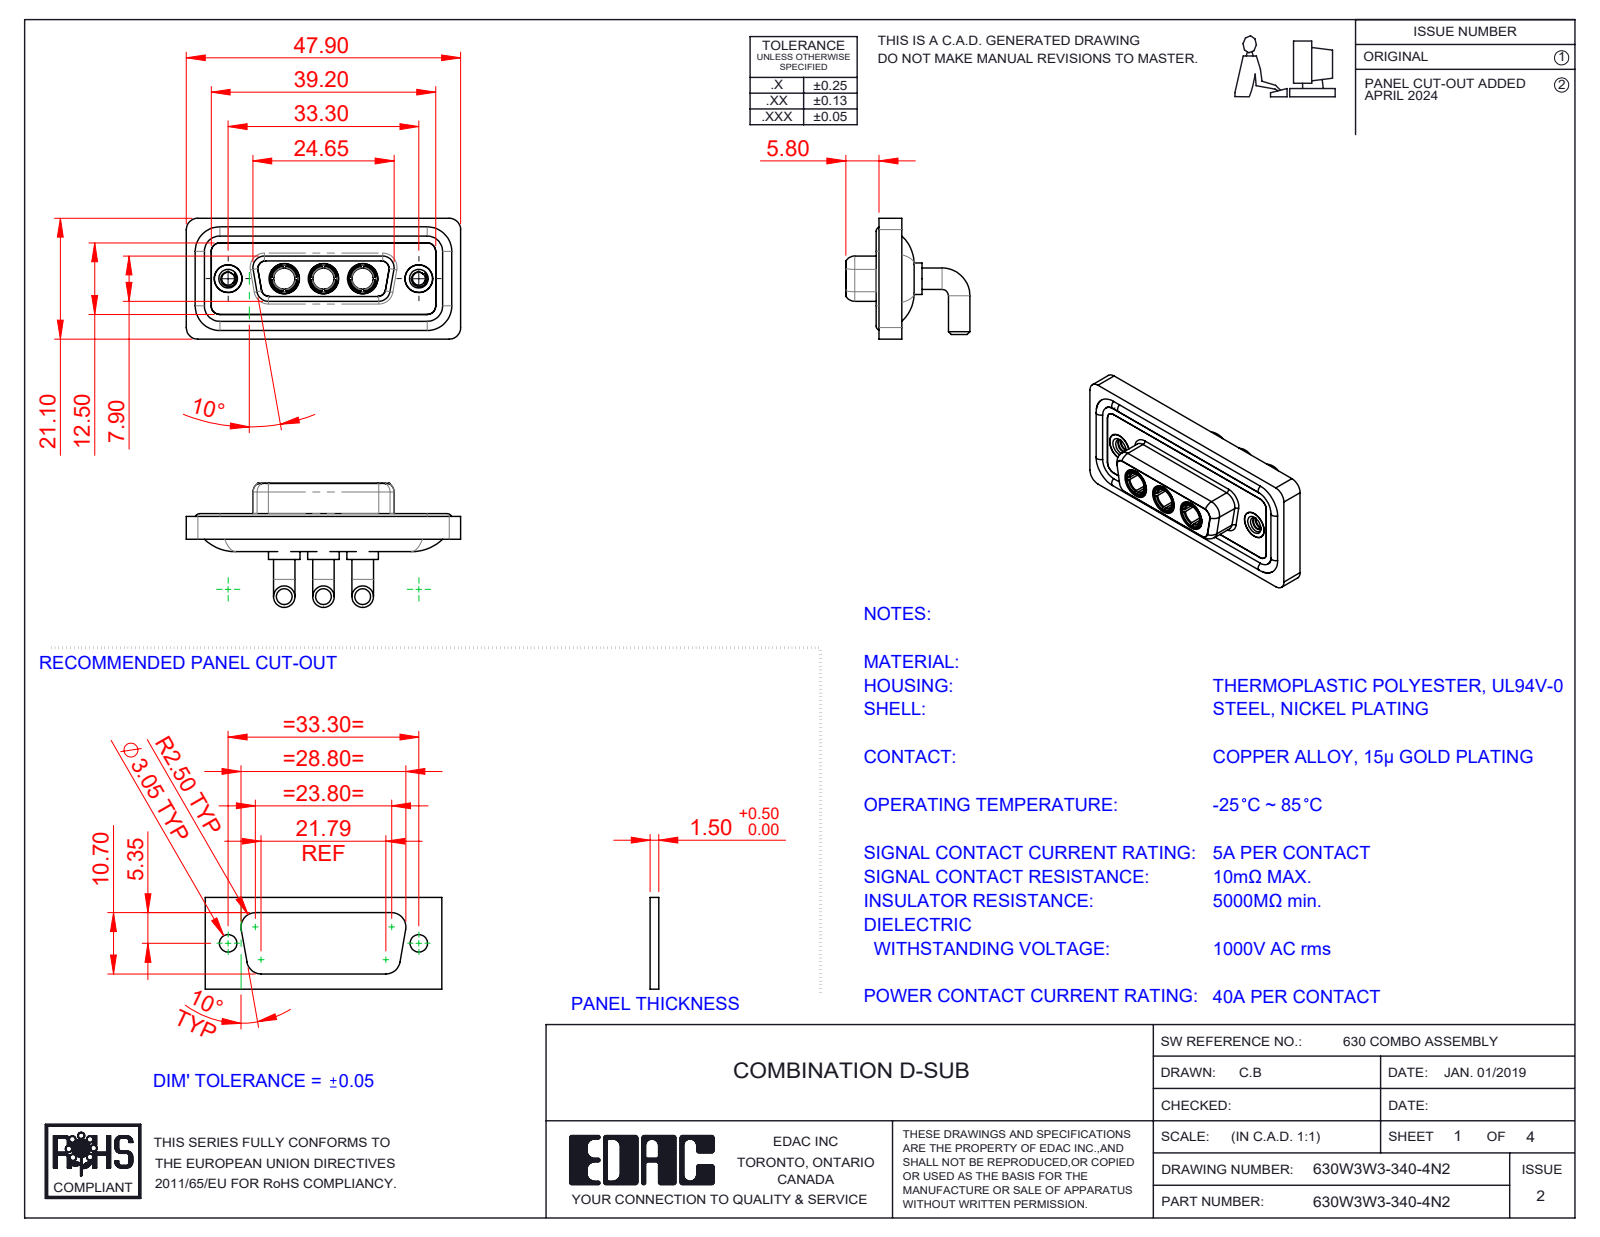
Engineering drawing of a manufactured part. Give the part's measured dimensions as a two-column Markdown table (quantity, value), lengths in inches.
| quantity | value |
| --- | --- |
| part name | Power Socket_40A RA; 630Combo Housing_3W3; 630Combo Shell Rear_15 Contacts; 630Combo Shell Front_15 Contacts (+3 more) |
| STEP written by | SolidWorks 2023 (CONFIG_CONTROL_DESIGN) |
| units | inches |
| bodies | 13 solids, 620 faces (192 planar, 263 cylindrical, 165 other) |
| overall size | 1.886 × 0.854 × 0.831 |
| volume | 0.39 in³ |
| surface area | 15.66 in² |
| round holes (diameter × count) | 0.191 × 5, 0.146 × 3, 0.209 × 3, 0.089 × 2, 0.157 × 2, 0.159 × 2, 0.197 × 2 |
| round bosses / shafts (diameter × count) | 0.148 × 6, 0.063 × 4, 0.217 × 3, 0.205 × 3, 0.195 × 3, 0.187 × 3, 0.195 × 2, 0.189 × 2 |
| partial cylindrical surfaces (radius × count) | 0.079 × 20, 0.059 × 18, 0.053 × 12, 0.063 × 8, 0.01 × 4, 0.02 × 4, 0.024 × 4, 0.026 × 4 |
| main face-to-face distances | 0.016, 0.071, 0.043, 0.063, 0.114, 0.098, 0.122, 0.146, 0.161, 0.059 |
| hole center spacings | 0.27, 0.386, 0.656, 0.925, 0.539, 1.311 |
